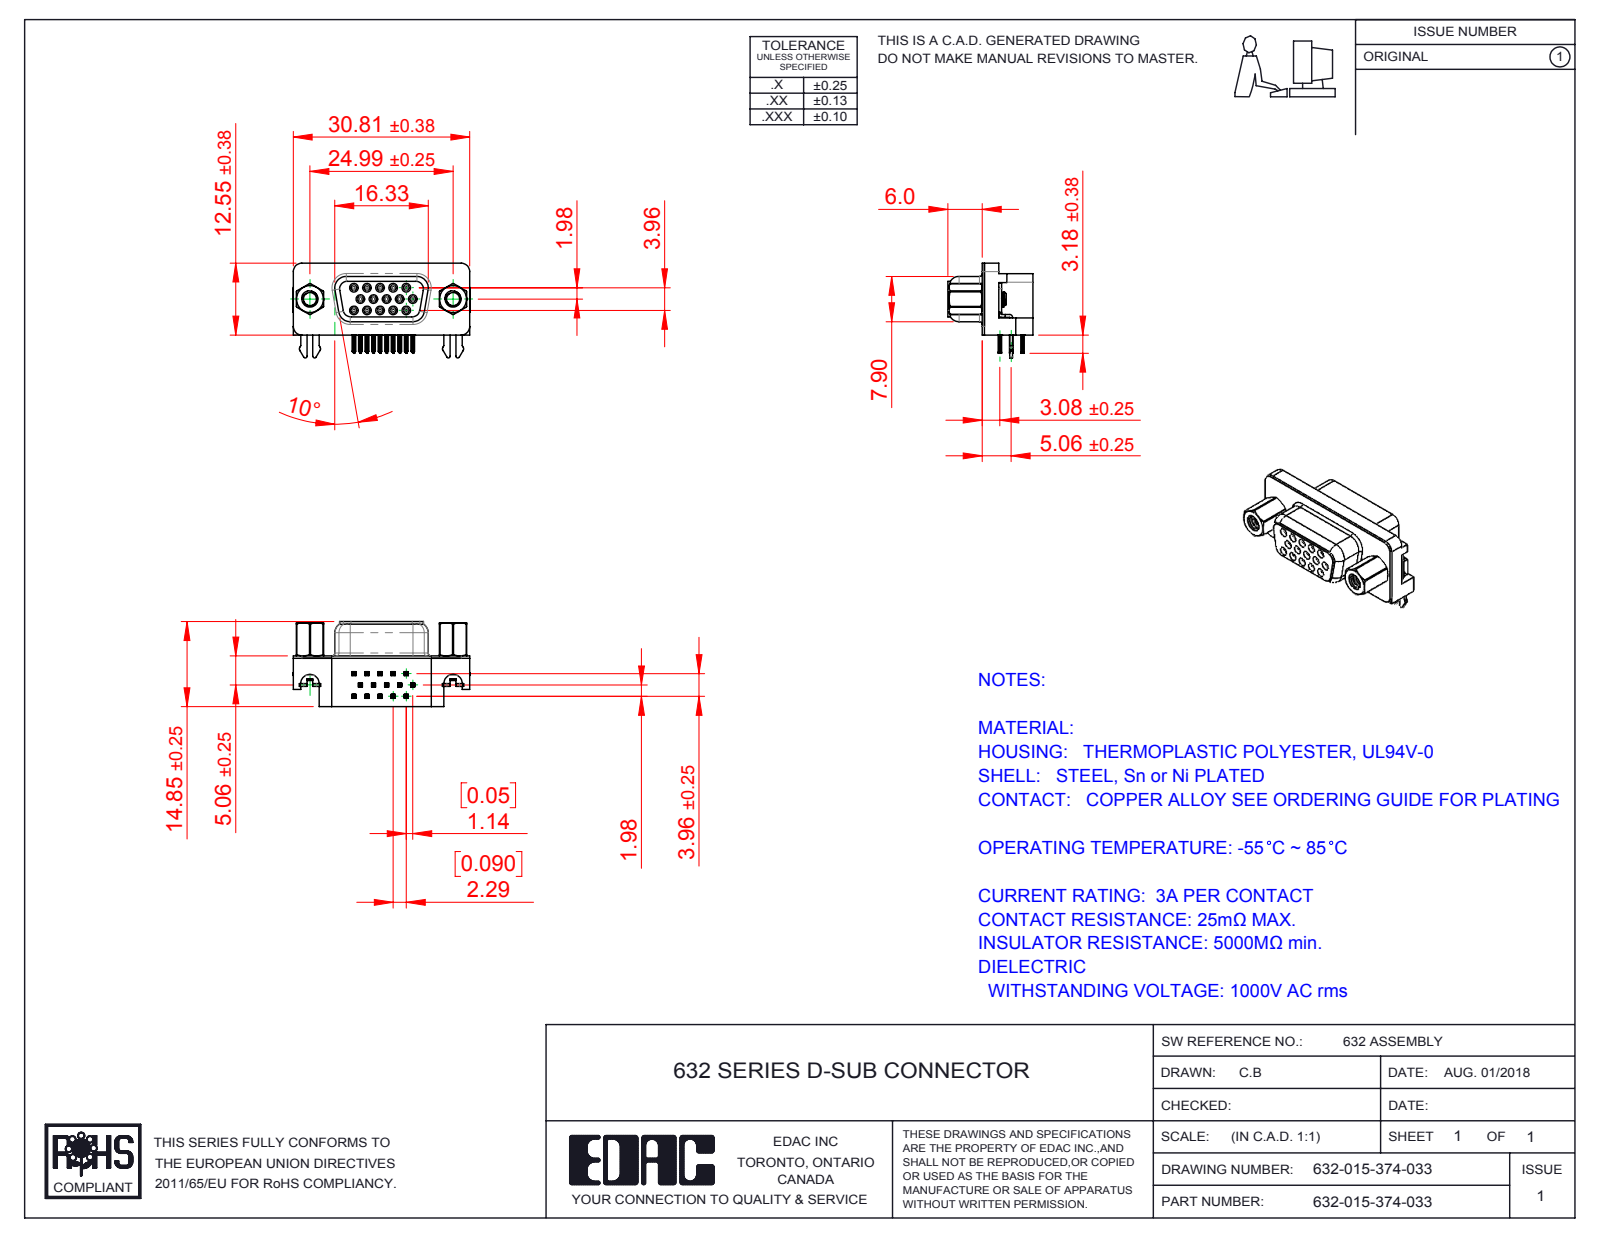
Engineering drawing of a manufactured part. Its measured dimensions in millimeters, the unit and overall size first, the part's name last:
Units: millimetres
Overall size (bounding box): 30.89 × 16.55 × 14.85
Round holes (diameter × count): ⌀0.8 ×15, ⌀0.9 ×15, ⌀2.29 ×2, ⌀4 ×2, ⌀4.8 ×2, ⌀5 ×2
Round bosses / shafts (diameter × count): ⌀1.2 ×15, ⌀4.9 ×2, ⌀2.79 ×2
Partial cylindrical surfaces — rounded edges, fillets, slot ends (radius × count): R0.1 ×120, R0.15 ×60, R0.35 ×30, R0.34 ×15, R1 ×11, R0.28 ×10, R0.5 ×10, R1.35 ×8
Main face-to-face distances: 0.4, 1.98, 8.45, 8.85, 2.9, 2.5, 5.95, 6.7, 7.05, 3.17
Hole centre spacings: 2.28, 2.29, 3.96, 4.57, 6.05, 3.97, 4.58, 6.86
Volume: 3 051 mm³ · Surface area: 5 177 mm²
Bodies: 21 solids, 2376 faces (996 planar, 646 cylindrical, 734 other)
Part name (STEP PRODUCT): 632 Contact Top; 632 Shell_9 Socket; 632 Housing_15 Socket; 632 2 Prong Board Lock (+5 more)
STEP written by: SolidWorks 2016 (CONFIG_CONTROL_DESIGN)
